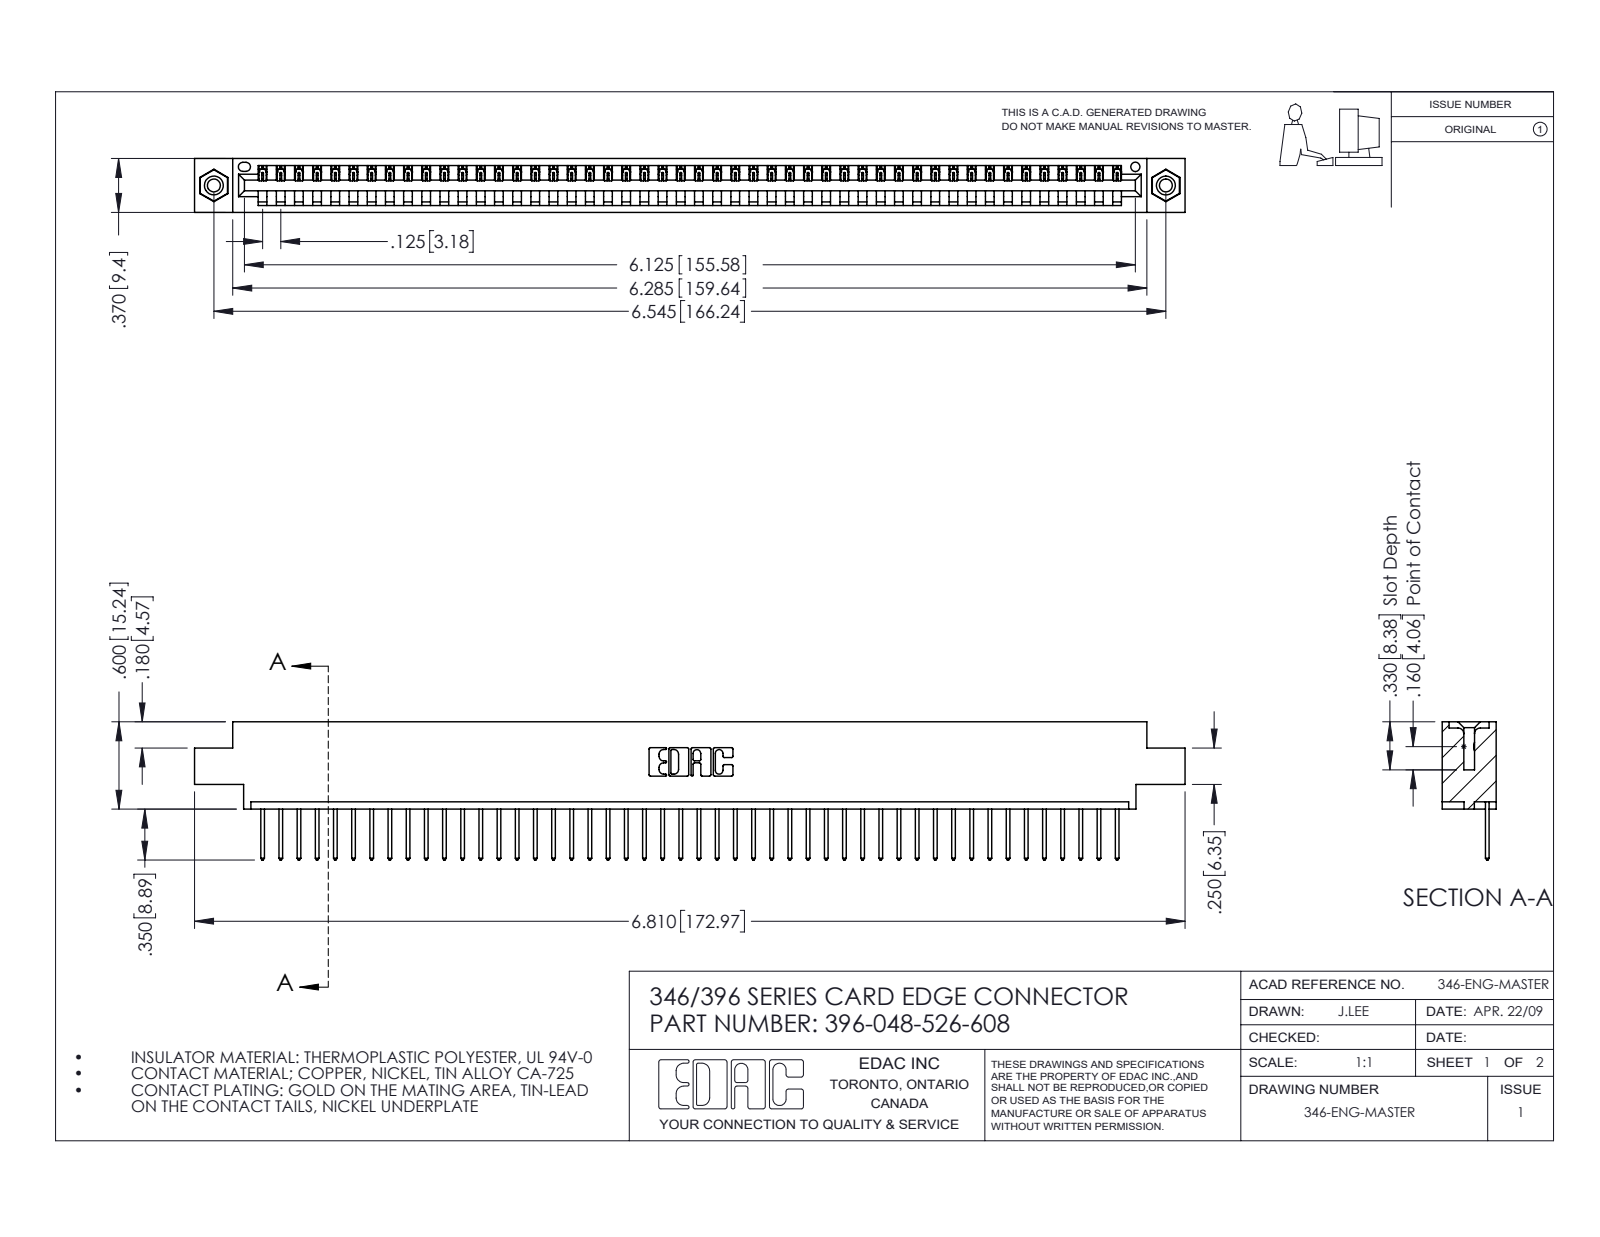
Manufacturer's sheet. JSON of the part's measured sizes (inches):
{"part_name": "345-292-001_345-293-126; 346 Part_0.170 Offset - 0.156 Dia-TI; 396-048-526-608; 345-250-001_345-250-003-102", "step_written_by": "SolidWorks 2016 (CONFIG_CONTROL_DESIGN)", "units": "inches", "bodies": {"solids": 51, "faces": 2970, "planar": 2032, "cylindrical": 922, "other": 16}, "overall_size": [6.81, 0.95, 0.37], "volume_in3": 1.001, "surface_area_in2": 32.08, "round_holes": [[0.089, 2], [0.125, 2], [0.156, 2], [0.064, 1]], "round_bosses_or_shafts": [[0.155, 2]], "partial_cylinders_radius": [[0.006, 96], [0.01, 96], [0.01, 22], [0.007, 6], [0.031, 6], [0.026, 3], [0.031, 2], [0.04, 2]], "face_to_face_distances": [0.048, 0.322, 0.37, 0.25, 0.072, 0.298, 0.025, 0.222, 0.148, 0.1], "hole_center_spacings": [0.246, 6.336, 6.545]}
